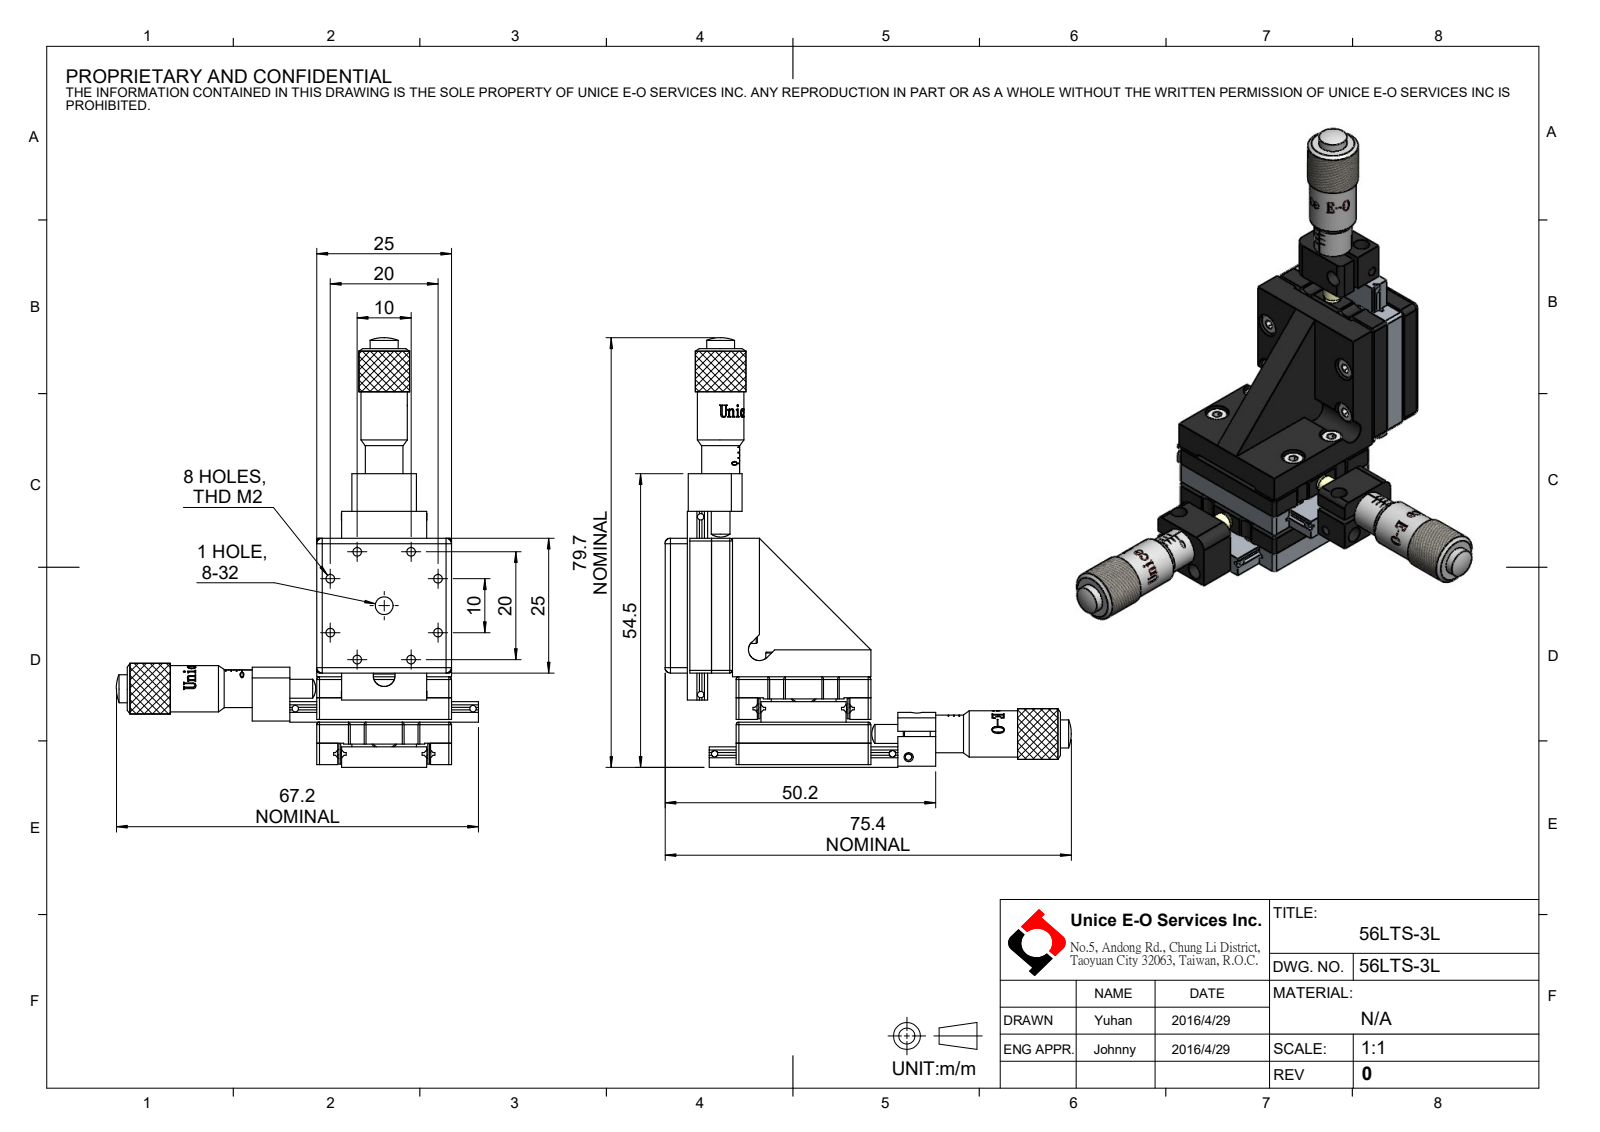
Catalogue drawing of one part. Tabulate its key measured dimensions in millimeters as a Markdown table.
| quantity | value |
| --- | --- |
| part name | 56LTS-3L |
| STEP written by | SolidWorks 2016 (CONFIG_CONTROL_DESIGN) |
| units | millimeters |
| bodies | 73 solids, 2750 faces (1124 planar, 1026 cylindrical, 600 other) |
| overall size | 79.7 × 75.4 × 67.2 |
| volume | 28 678 mm³ |
| surface area | 30 420 mm² |
| round holes (diameter × count) | 1.1 × 30, 1.8 × 27, 3.1 × 18, 1.6 × 16, 2.4 × 16, 1.2 × 12, 3 × 12, 4 × 12, 4.4 × 8, 1.7 × 3, 2.5 × 3, 2.6 × 3 |
| round bosses / shafts (diameter × count) | 1.5 × 35, 2 × 8, 4 × 4, 9.4 × 3, 8.6 × 3, 7 × 3, 6.4 × 3, 5.7 × 3 |
| partial cylindrical surfaces (radius × count) | 0.5 × 44, 2 × 22, 0.75 × 14, 1 × 11, 4.28 × 3 |
| main face-to-face distances | 8.4, 4.6, 0.5, 8.9, 4.5, 0.7, 4.1, 4.3, 3.8, 3.9 |
| hole center spacings | 11.18, 15.81, 4.04, 5.03, 5.64, 9, 11.44, 13.87 |
